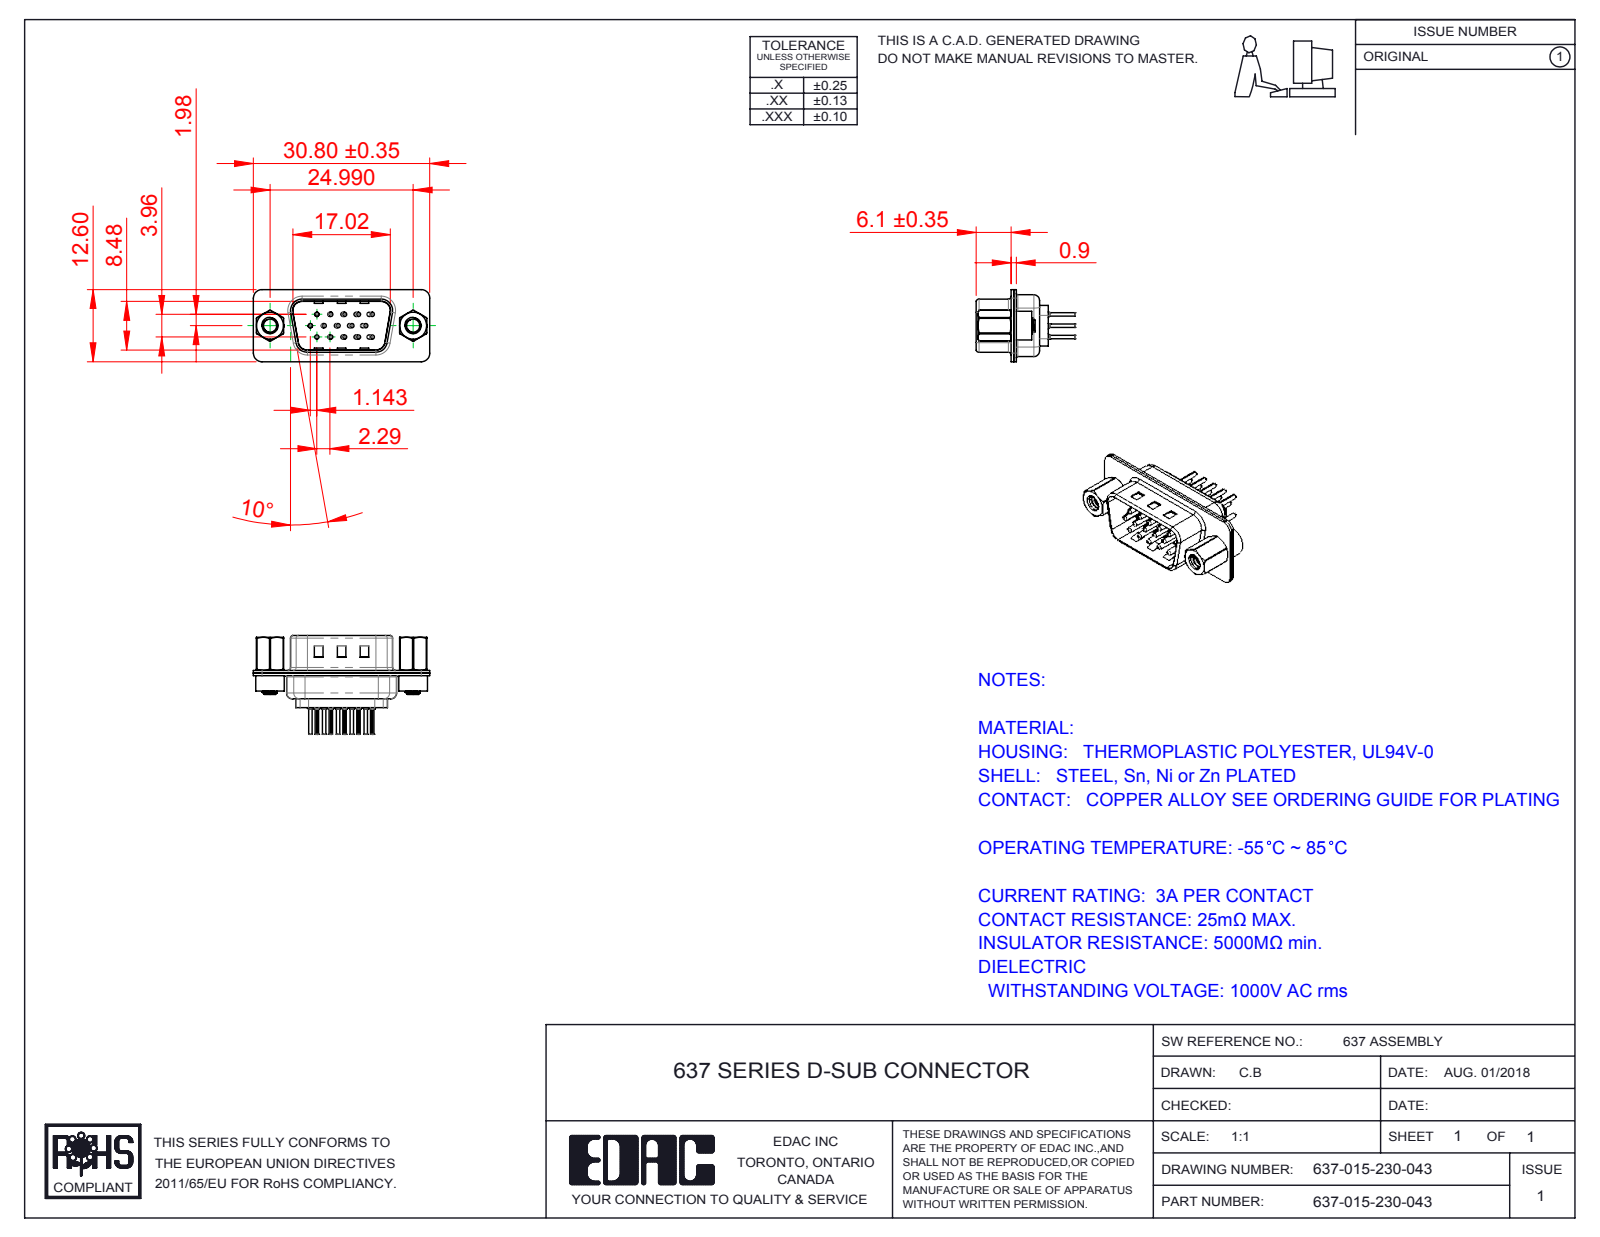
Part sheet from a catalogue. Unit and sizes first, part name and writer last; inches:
Units: inches
Overall size (bounding box): 1.213 × 0.679 × 0.496
Round holes (diameter × count): ⌀0.063 ×27, ⌀0.008 ×15, ⌀0.014 ×15, ⌀0.043 ×15, ⌀0.03 ×12, ⌀0.079 ×12, ⌀0.089 ×2, ⌀0.09 ×2, ⌀0.157 ×2, ⌀0.189 ×2
Round bosses / shafts (diameter × count): ⌀0.079 ×15, ⌀0.059 ×15, ⌀0.03 ×15, ⌀0.024 ×15, ⌀0.197 ×2, ⌀0.193 ×2, ⌀0.11 ×2
Partial cylindrical surfaces — rounded edges, fillets, slot ends (radius × count): R0.004 ×30, R0.059 ×16, R0.079 ×12, R0.02 ×8, R0.01 ×4, R0.022 ×4, R0.028 ×4, R0.037 ×4
Main face-to-face distances: 0.018, 0.035, 0.016, 0.334, 0.028, 0.35, 0.012, 0.179, 0.041, 0.256
Hole centre spacings: 0.156, 0.09, 0.09, 0.18, 0.095, 0.238, 0.191, 0.093
Volume: 0.093 in³ · Surface area: 7.952 in²
Bodies: 22 solids, 1930 faces (489 planar, 756 cylindrical, 685 other)
Part name (STEP PRODUCT): 637 Shell Rear_15 Contacts; 637 4-40 Threaded Rivet; 637 Shell Front_15 Contacts; 637 Contact Row 1_30 (+5 more)
STEP written by: SolidWorks 2016 (CONFIG_CONTROL_DESIGN)
